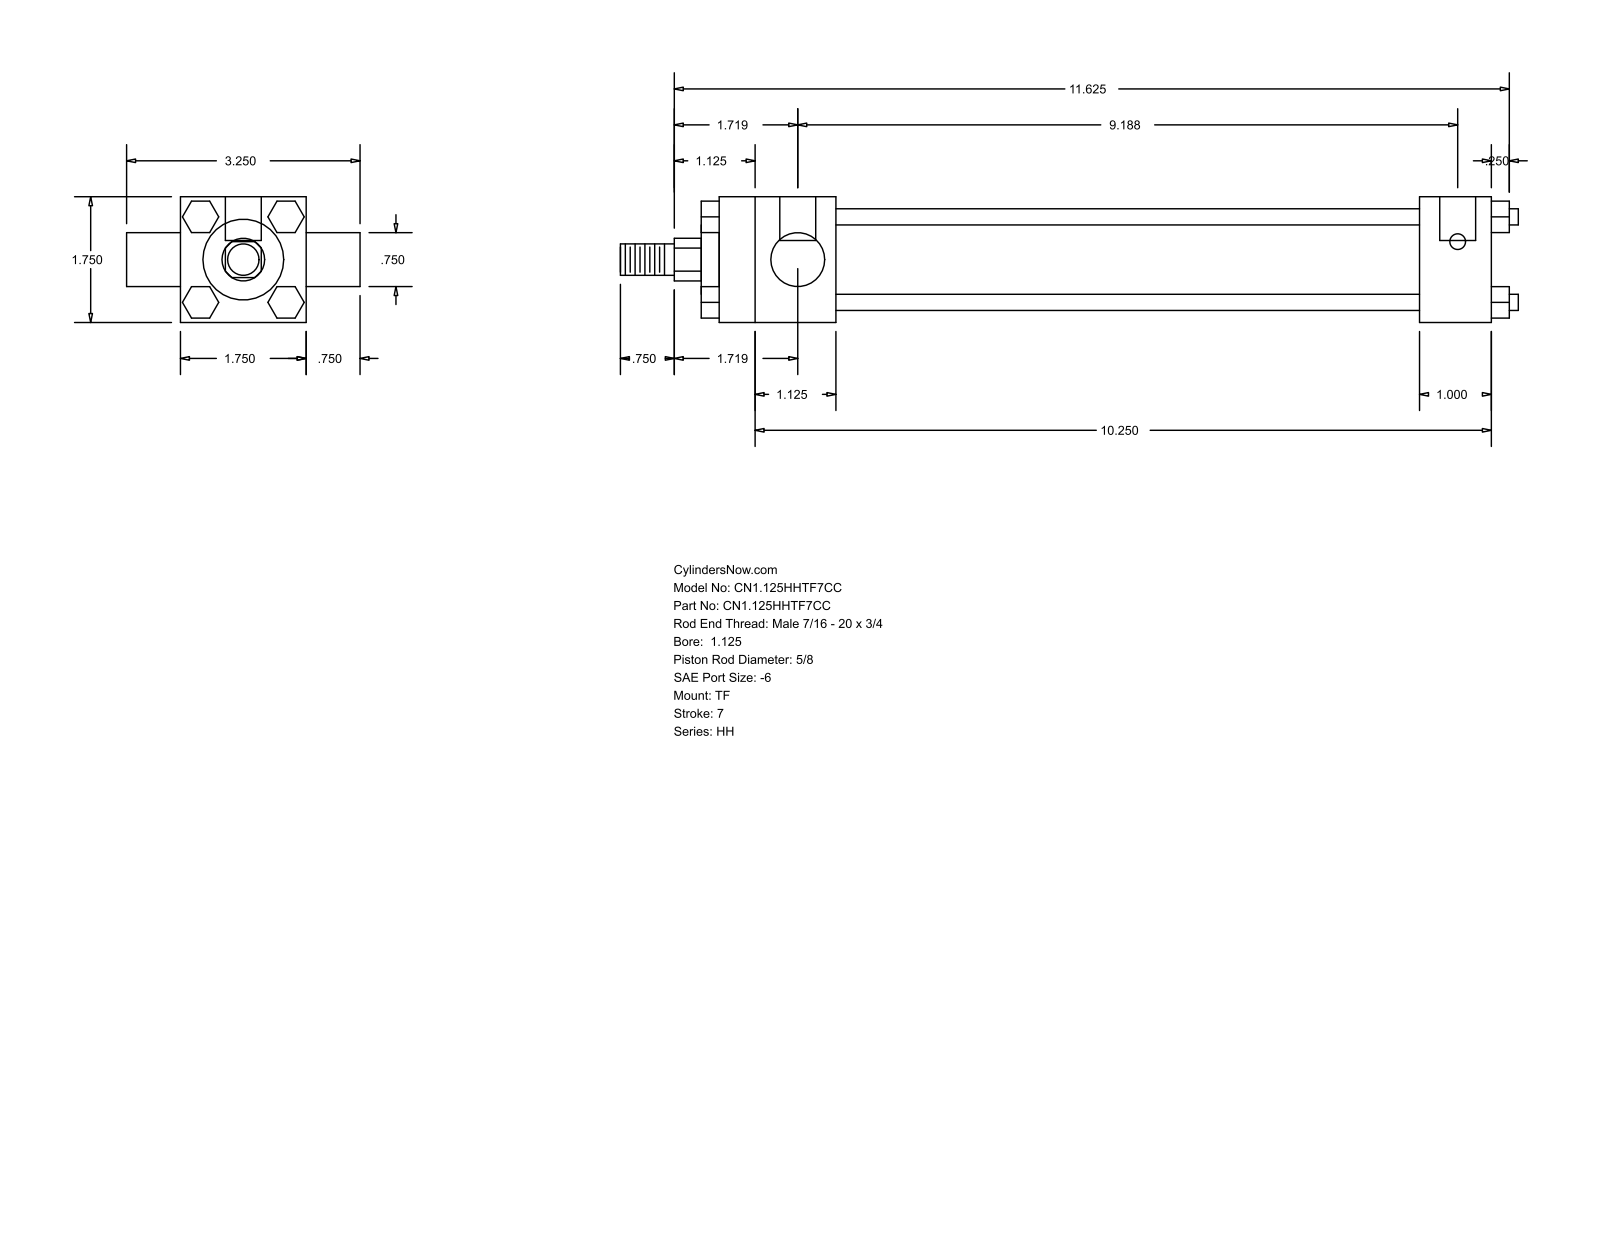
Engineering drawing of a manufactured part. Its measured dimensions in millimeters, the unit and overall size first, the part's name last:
Units: millimetres
Overall size (bounding box): 317.5 × 82.55 × 44.45
Round holes (diameter × count): ⌀5.56 ×3, ⌀12.7 ×2
Round bosses / shafts (diameter × count): ⌀5.71 ×4, ⌀34.92 ×1, ⌀28.57 ×1, ⌀19.05 ×1, ⌀15.88 ×1, ⌀11.11 ×1
Partial cylindrical surfaces — rounded edges, fillets, slot ends (radius × count): R7.54 ×1
Main face-to-face distances: 44.46, 11.11, 206.37, 231.78, 25.41, 41.27, 247.64, 273.05, 47.62, 6.35
Hole centre spacings: 3.17, 230.19, 233.36
Bodies: 0 solids, 120 faces (92 planar, 28 cylindrical, 0 other)
Part name (STEP PRODUCT): HH_TF__0112_0.625
STEP written by: GSSL Pune (CONFIG_CONTROL_DESIGN)
